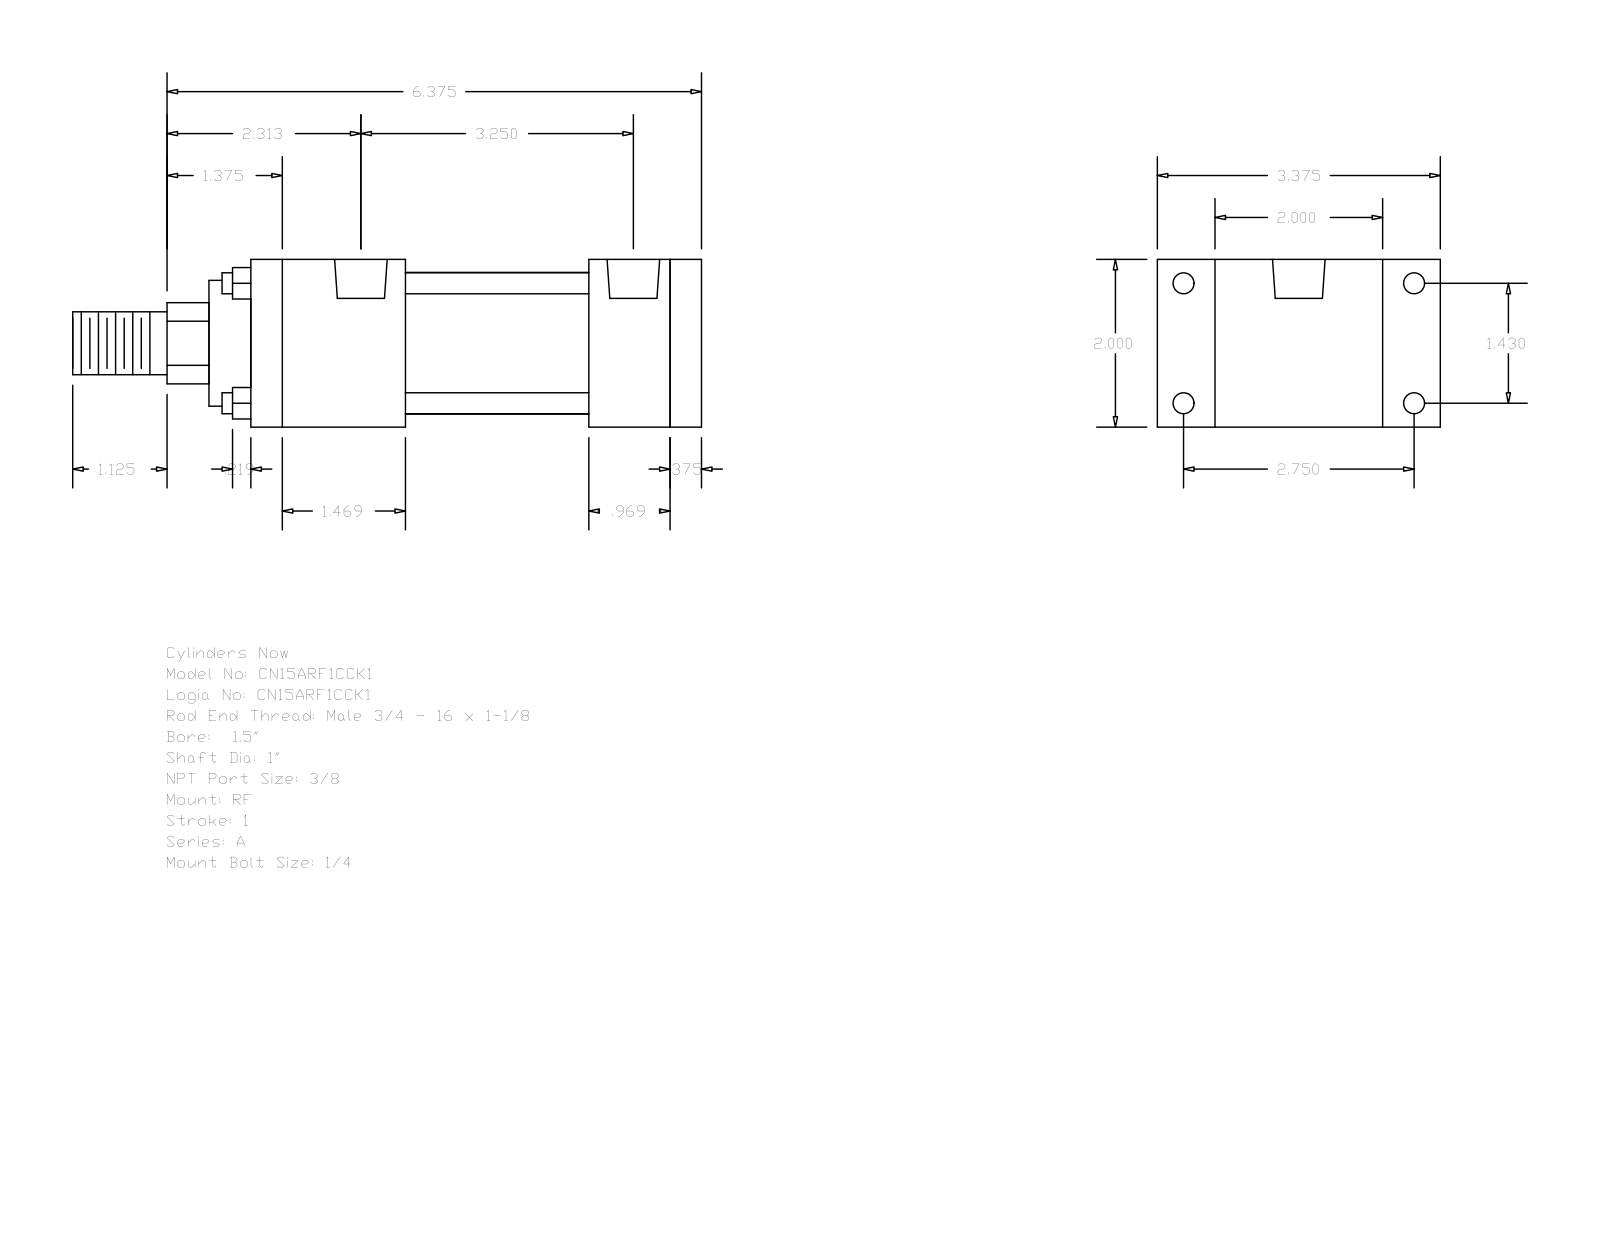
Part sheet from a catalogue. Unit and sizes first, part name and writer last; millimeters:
Units: millimetres
Overall size (bounding box): 190.5 × 85.72 × 50.8
Round holes (diameter × count): ⌀5.56 ×4, ⌀6.35 ×4, ⌀15.93 ×2
Round bosses / shafts (diameter × count): ⌀6.35 ×4, ⌀42.93 ×1, ⌀38.1 ×1, ⌀25.4 ×1, ⌀19.05 ×1
Partial cylindrical surfaces — rounded edges, fillets, slot ends (radius × count): R12.29 ×1
Main face-to-face distances: 50.8, 9.53, 55.56, 127, 136.53, 102.39, 24.61, 34.14, 46.83, 80.17
Hole centre spacings: 3.97, 36.32, 69.84, 74.61, 78.58, 78.72, 82.55
Bodies: 0 solids, 92 faces (64 planar, 28 cylindrical, 0 other)
Part name (STEP PRODUCT): A_RF__0150_1
STEP written by: GSSL Pune (CONFIG_CONTROL_DESIGN)
